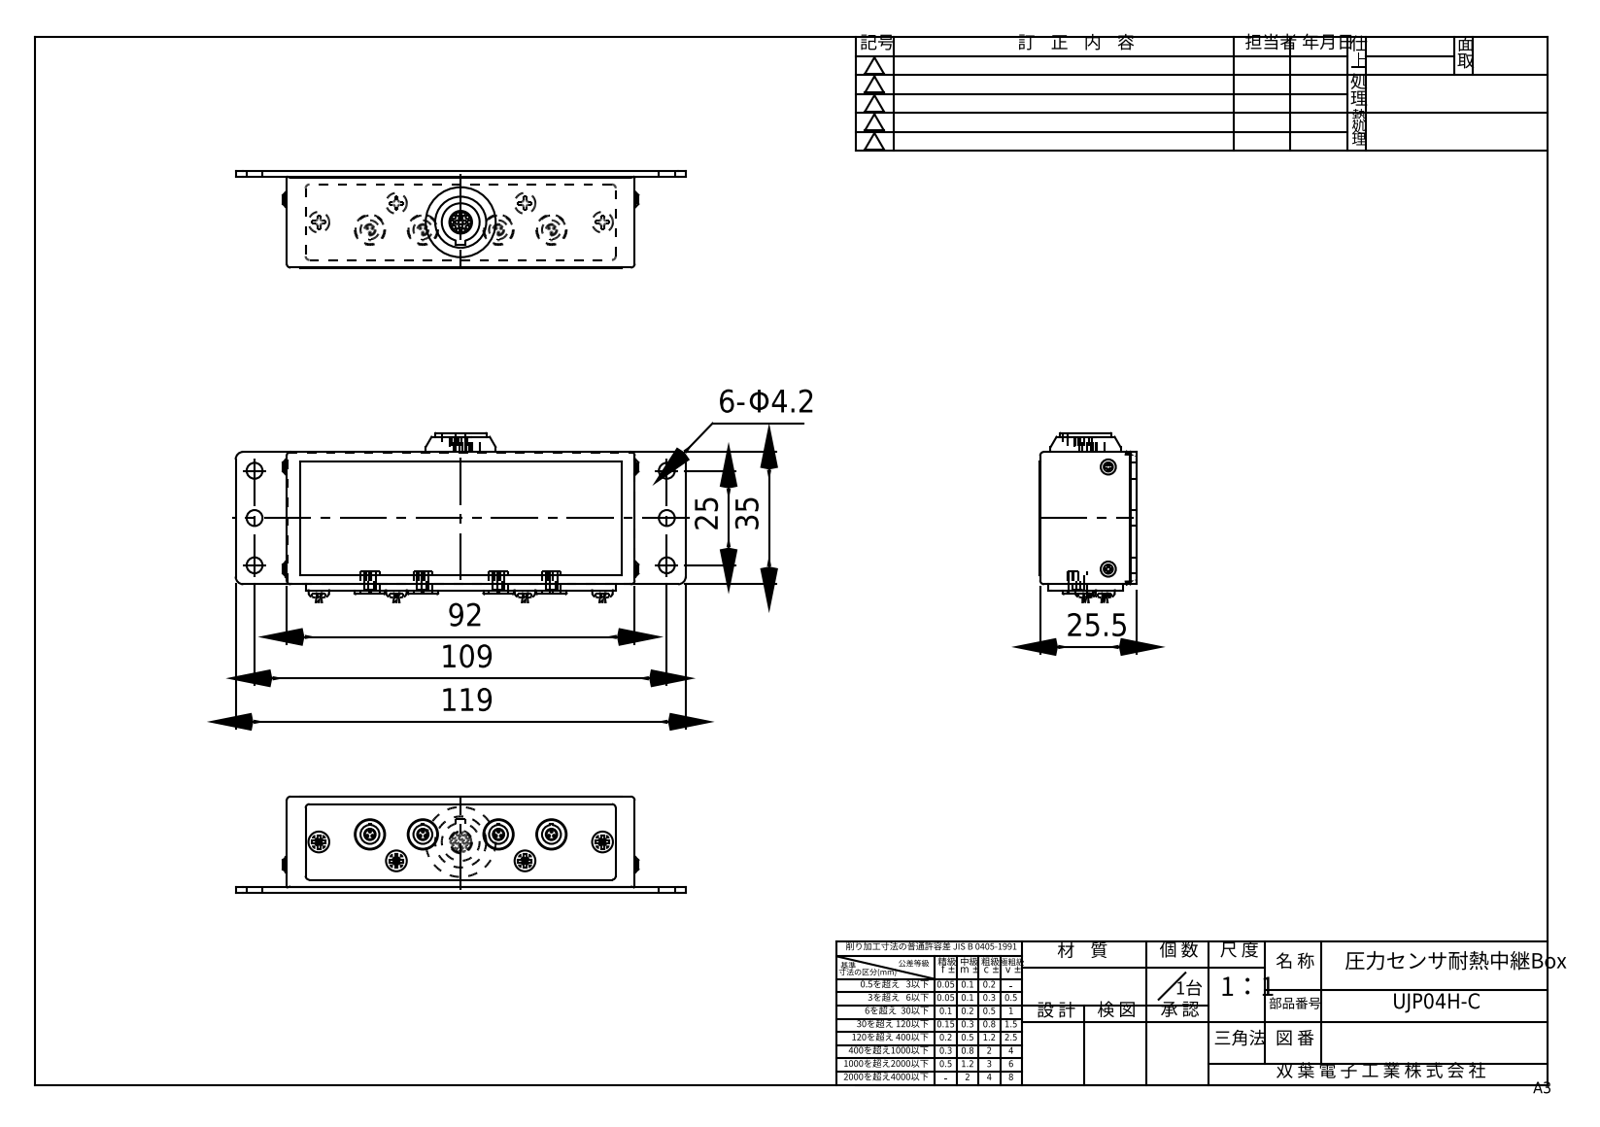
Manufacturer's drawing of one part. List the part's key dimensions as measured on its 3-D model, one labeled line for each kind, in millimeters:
STEP written by: XStep 1.0 (automotive_design)
Units: millimetres
Bodies: 1 solid, 323 faces (186 planar, 104 cylindrical, 33 other)
Overall size (bounding box): 119 × 43.56 × 25.6
Volume: 86 971 mm³ · Surface area: 16 652 mm²
Round holes (diameter × count): ⌀1 ×14, ⌀0.6 ×12, ⌀4.2 ×6, ⌀5 ×4, ⌀10 ×1
Round bosses / shafts (diameter × count): ⌀8 ×4, ⌀3 ×4, ⌀4 ×2, ⌀18.5 ×1, ⌀13.5 ×1, ⌀6 ×1
Partial cylindrical surfaces — rounded edges, fillets, slot ends (radius × count): R0.55 ×16, R1 ×12, R0.2 ×8, R2 ×4, R2.75 ×4
Main face-to-face distances: 25.6, 36.6, 1.5, 24.1, 92, 1.6, 35, 25.5, 24, 2
Hole centre spacings: 0.8, 1.38, 2.25, 3.64, 4.28, 14, 34, 1.39
